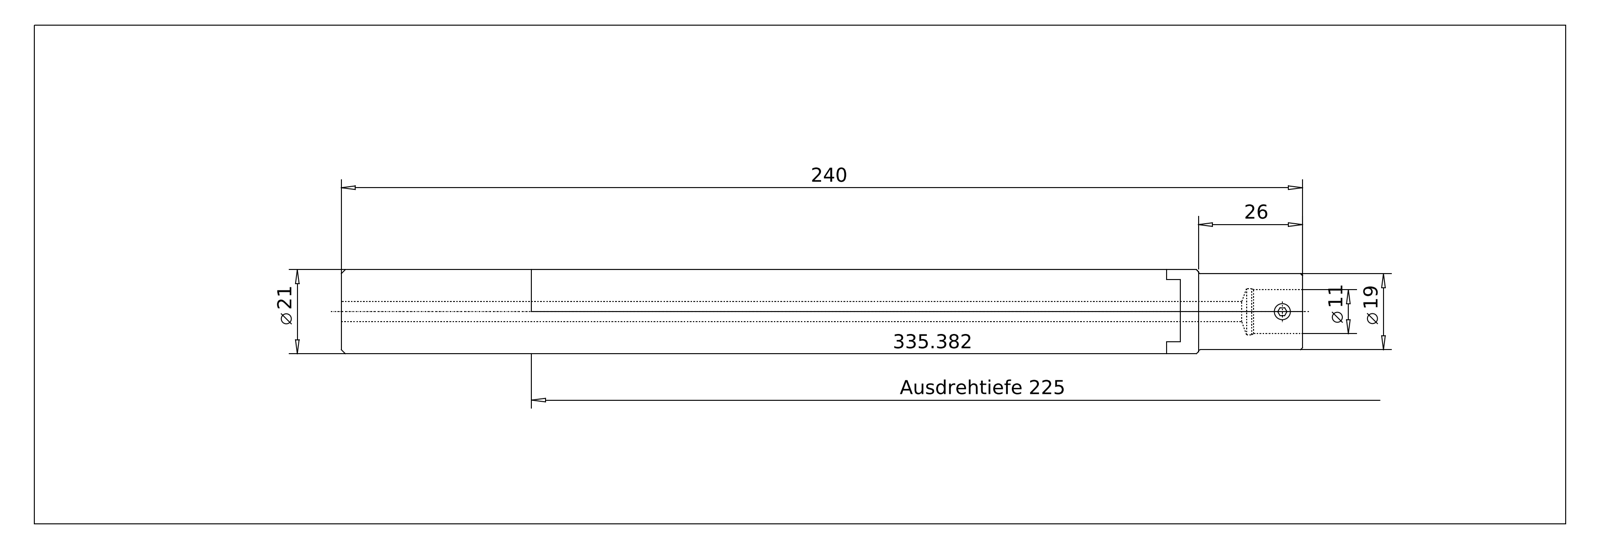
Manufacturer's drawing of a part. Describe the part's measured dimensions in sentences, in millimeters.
The part is named "335.382 Kaiser D21 X CK1 X 205HM|690.431 Kaiser ETL M4 X 5 CK1;NONE; 335.382 Kaiser D21 X CK1 X 205HM|335.382 Kaiser D21 X CK1 X 205HM;NONE". Its 3-D file was written by "ACIS (automotive_design)". It is 2 solids with 72 faces: 27 planar, 18 cylindrical and 27 other. Overall it measures 240 by 21 by 21 millimeters. Its volume is 75 544 cubic millimeters and its surface area 20 415 square millimeters. Round holes: 1 of diameter 3.2, 1 of diameter 4.2, 1 of diameter 5, 1 of diameter 11, 1 of diameter 11.5. Round bosses or shafts: 1 of diameter 21, 1 of diameter 19, 1 of diameter 4. Partial cylindrical surfaces (rounded edges, fillets, slot ends): 2 of radius 1.5. The main face-to-face distances are 240, 9.34, 5.9, 234.1, 26, 20.1, 214, 5, 1.99, 4.05.
